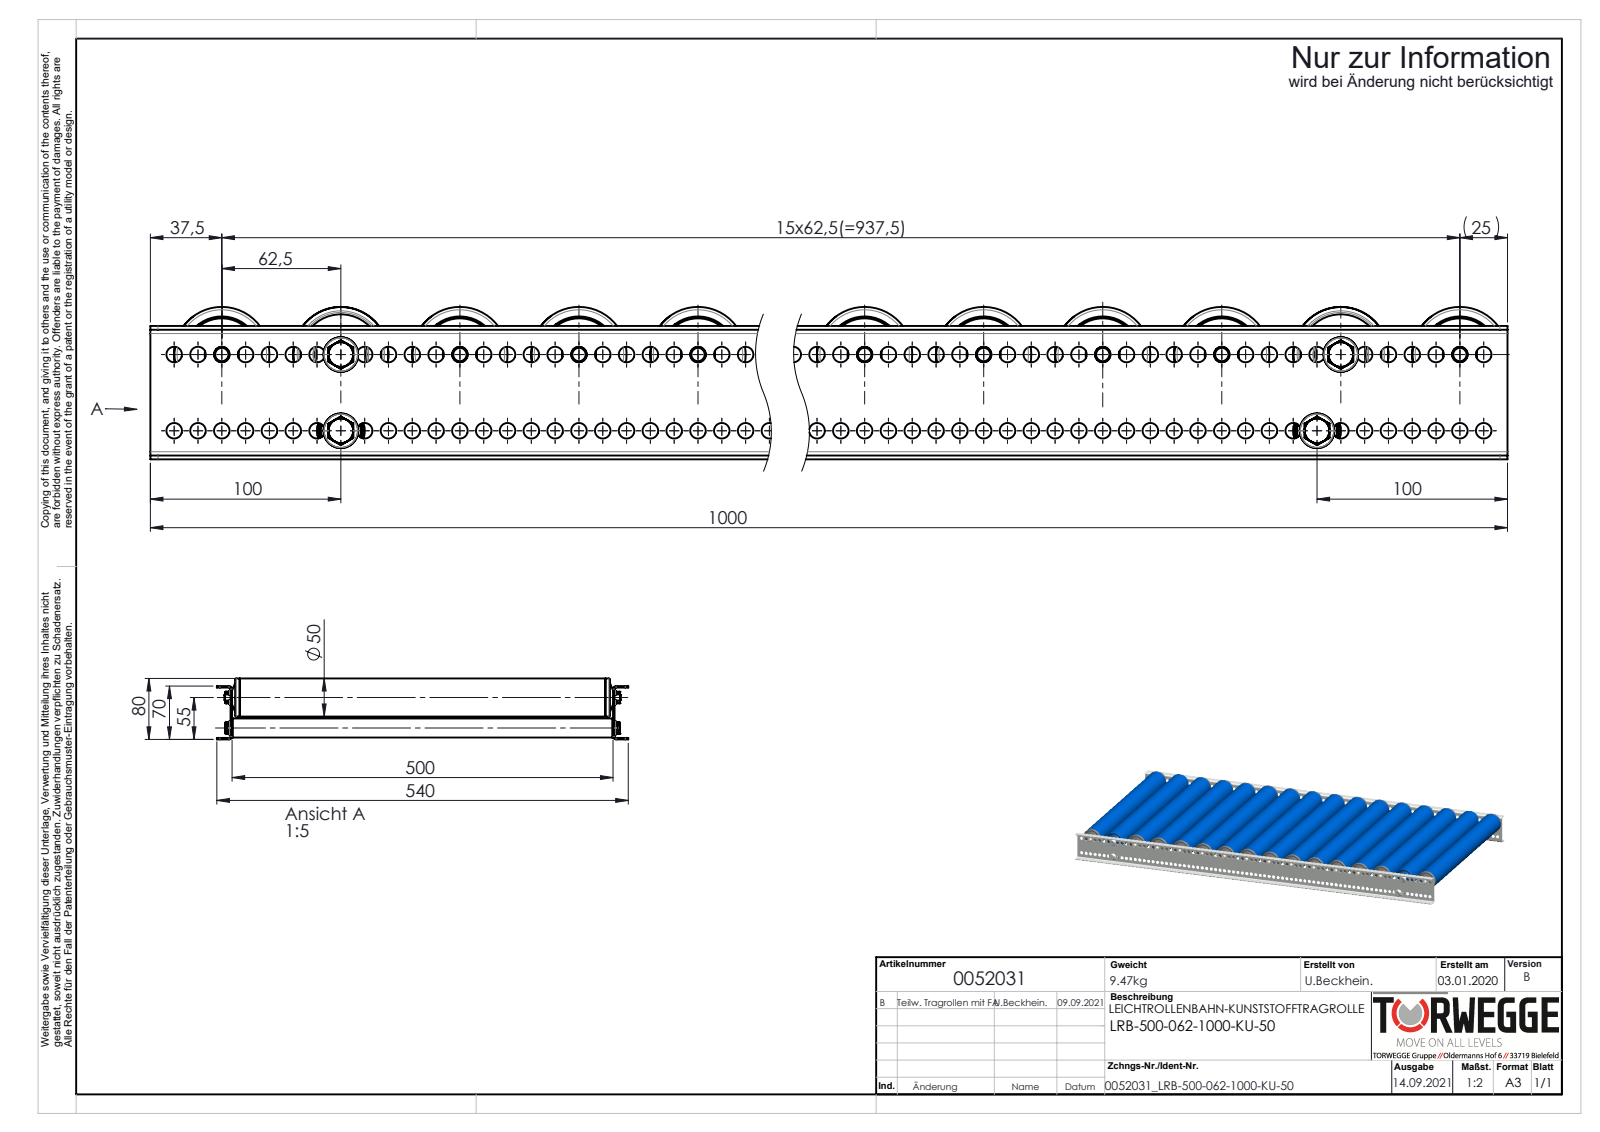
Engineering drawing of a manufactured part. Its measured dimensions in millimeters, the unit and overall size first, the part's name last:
Units: millimetres
Overall size (bounding box): 1000 × 540 × 80
Round holes (diameter × count): ⌀8.2 ×158, ⌀7.6 ×14, ⌀8 ×14, ⌀25 ×14, ⌀30 ×14, ⌀35 ×14, ⌀39.4 ×14, ⌀40 ×14, ⌀6.8 ×4, ⌀12 ×2, ⌀12.1 ×2, ⌀16 ×2
Round bosses / shafts (diameter × count): ⌀50 ×16, ⌀44.4 ×14, ⌀38 ×14, ⌀36 ×14, ⌀33 ×14, ⌀22 ×14, ⌀21 ×14, ⌀25 ×4
Partial cylindrical surfaces — rounded edges, fillets, slot ends (radius × count): R0.6 ×28, R0.75 ×28, R2.45 ×28, R4.87 ×14, R7 ×14, R4 ×8, R2 ×4, R2.5 ×4
Main face-to-face distances: 2, 502, 68, 500, 504, 492, 66, 70, 12, 6
Hole centre spacings: 12.5, 25, 37.5, 50, 62.5, 75, 87.5, 100
Volume: 5 085 000 mm³ · Surface area: 3 740 000 mm²
Bodies: 274 solids, 5068 faces (1336 planar, 2192 cylindrical, 1540 other)
Part name (STEP PRODUCT): S100994_Sperrzahnschraube_M08x16-8.8-A2K; 0017015_Tragrollenrohr-Ø50x2,8KU_KFG_0017015_L=485; Sicherungsring_DIN471_8x0.8_Circlip DIN 471 - 8 x 0.8; 0017015_Tragrollenrohr-Ø50x2,8KU_KFG_0017015_L=480 (+8 more)
STEP written by: SolidWorks 2020 (AUTOMOTIVE_DESIGN)
